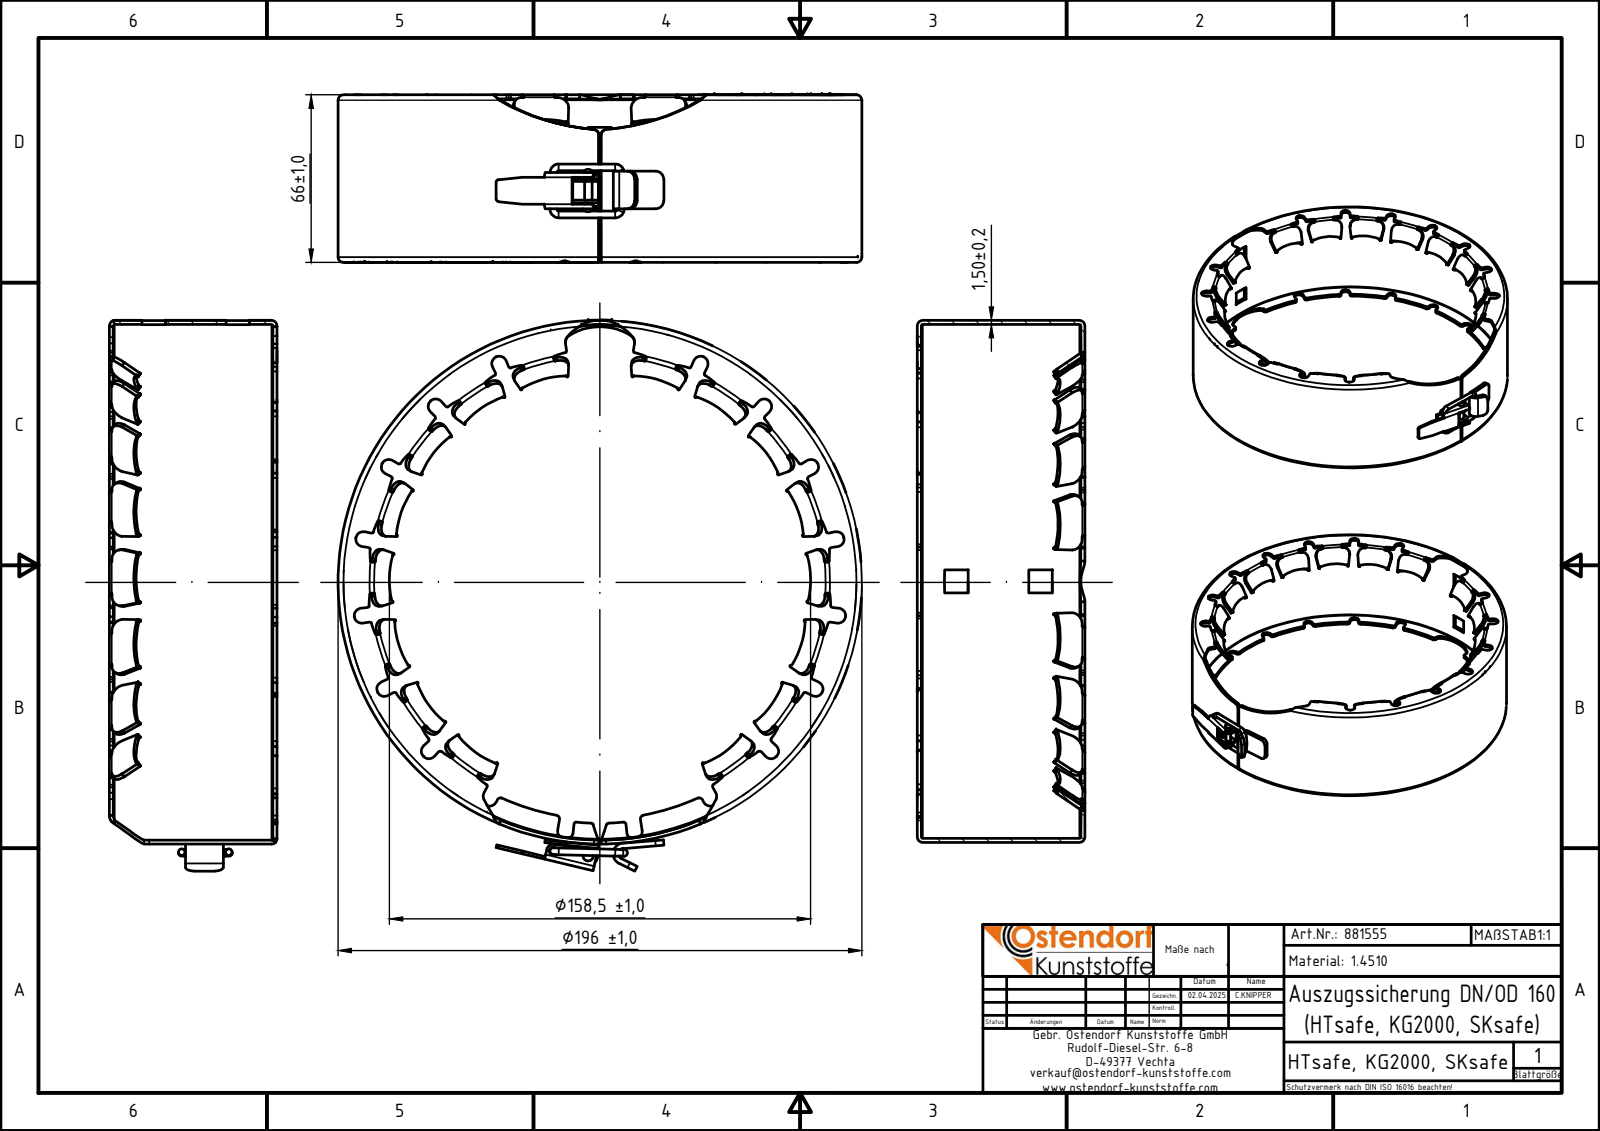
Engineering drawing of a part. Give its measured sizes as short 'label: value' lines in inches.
name: 881555z
written by: Autodesk Inventor 2024 (AUTOMOTIVE_DESIGN)
unit: in
bodies: 6 solids, 1080 faces (134 planar, 71 cylindrical, 875 other)
size: 8.051 × 7.656 × 2.449
volume: 4.491 in³; area: 158.5 in²
holes: 3× ⌀0.118, 1× ⌀7.538
bosses: 3× ⌀0.098, 1× ⌀7.656, 1× ⌀0.11
rounds: 5× R0.118, 4× R0.039, 2× R0.029, 2× R0.069, 2× R0.138, 1× R0.079, 1× R0.098, 1× R0.157
face distances: 0.039, 0.079, 0.04, 0.491, 0.315, 0.087, 0.404, 0.402, 0.089, 0.059
hole spacings: 0.197, 0.317, 0.514, 3.99, 3.991, 4.006
